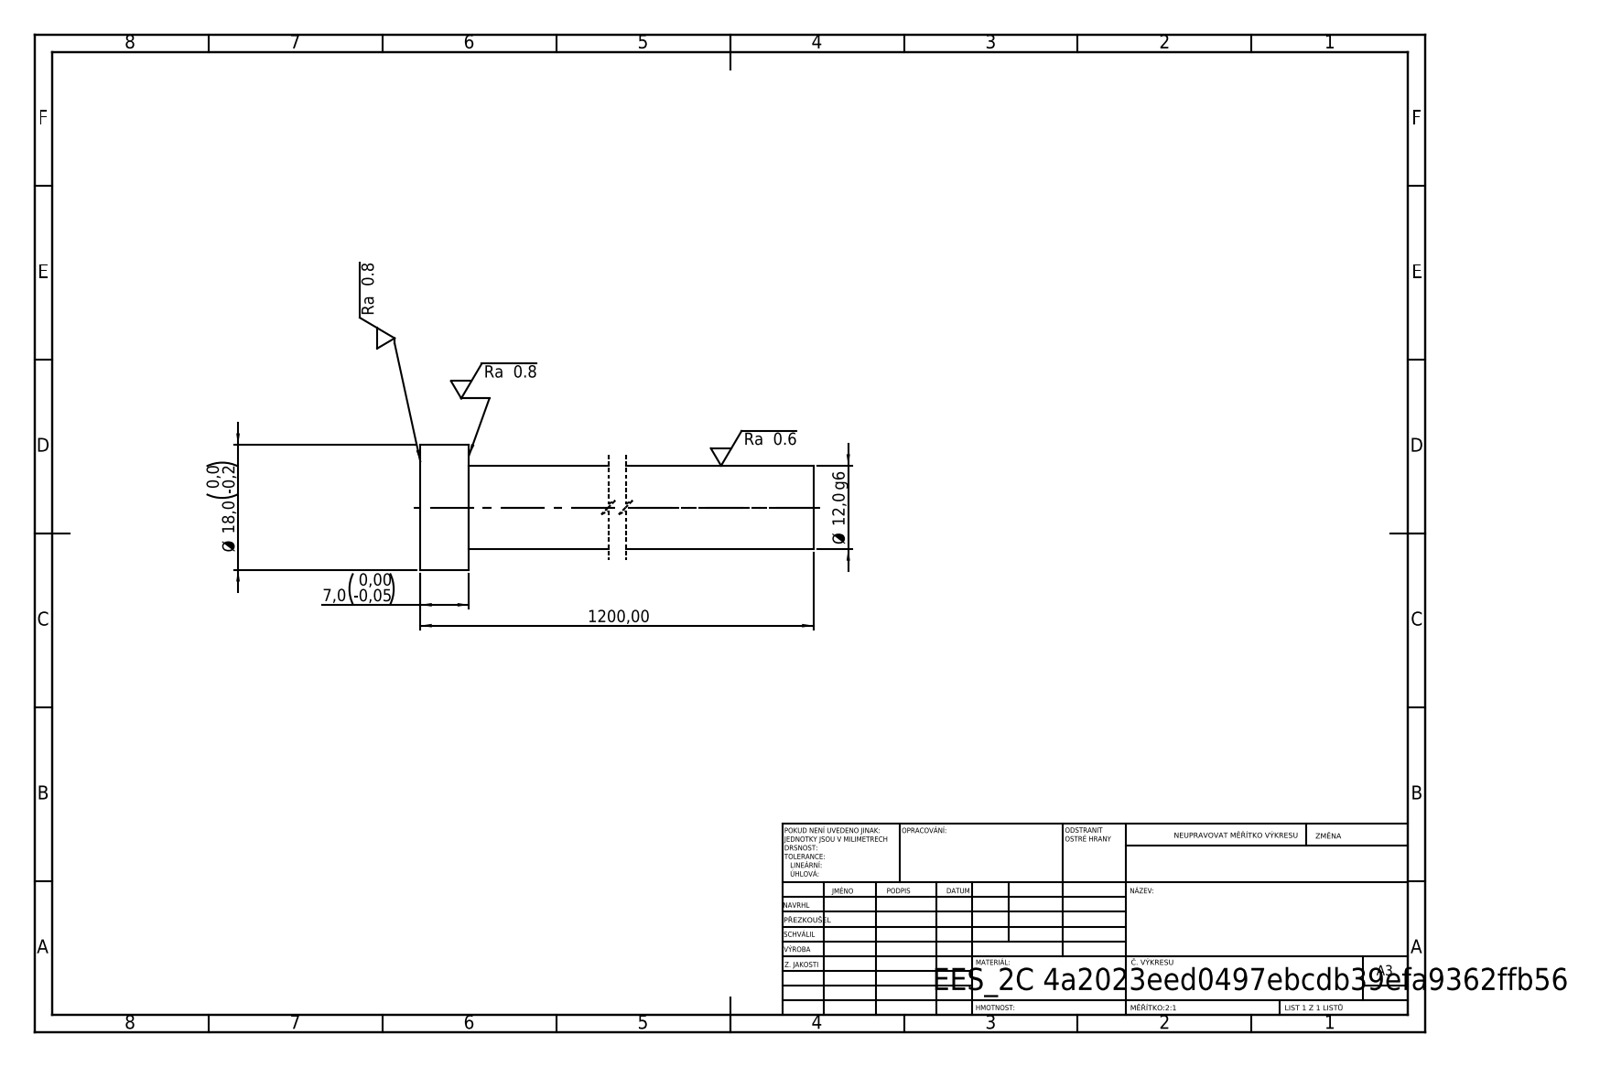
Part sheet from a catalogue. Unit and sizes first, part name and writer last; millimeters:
Units: millimetres
Overall size (bounding box): 1200 × 18 × 18
Round bosses / shafts (diameter × count): ⌀18 ×1, ⌀12 ×1
Main face-to-face distances: 7, 1200, 1193
Volume: 136 706 mm³ · Surface area: 45 880 mm²
Bodies: 1 solid, 7 faces (3 planar, 4 cylindrical, 0 other)
STEP written by: SolidWorks 2019 (CONFIG_CONTROL_DESIGN)
